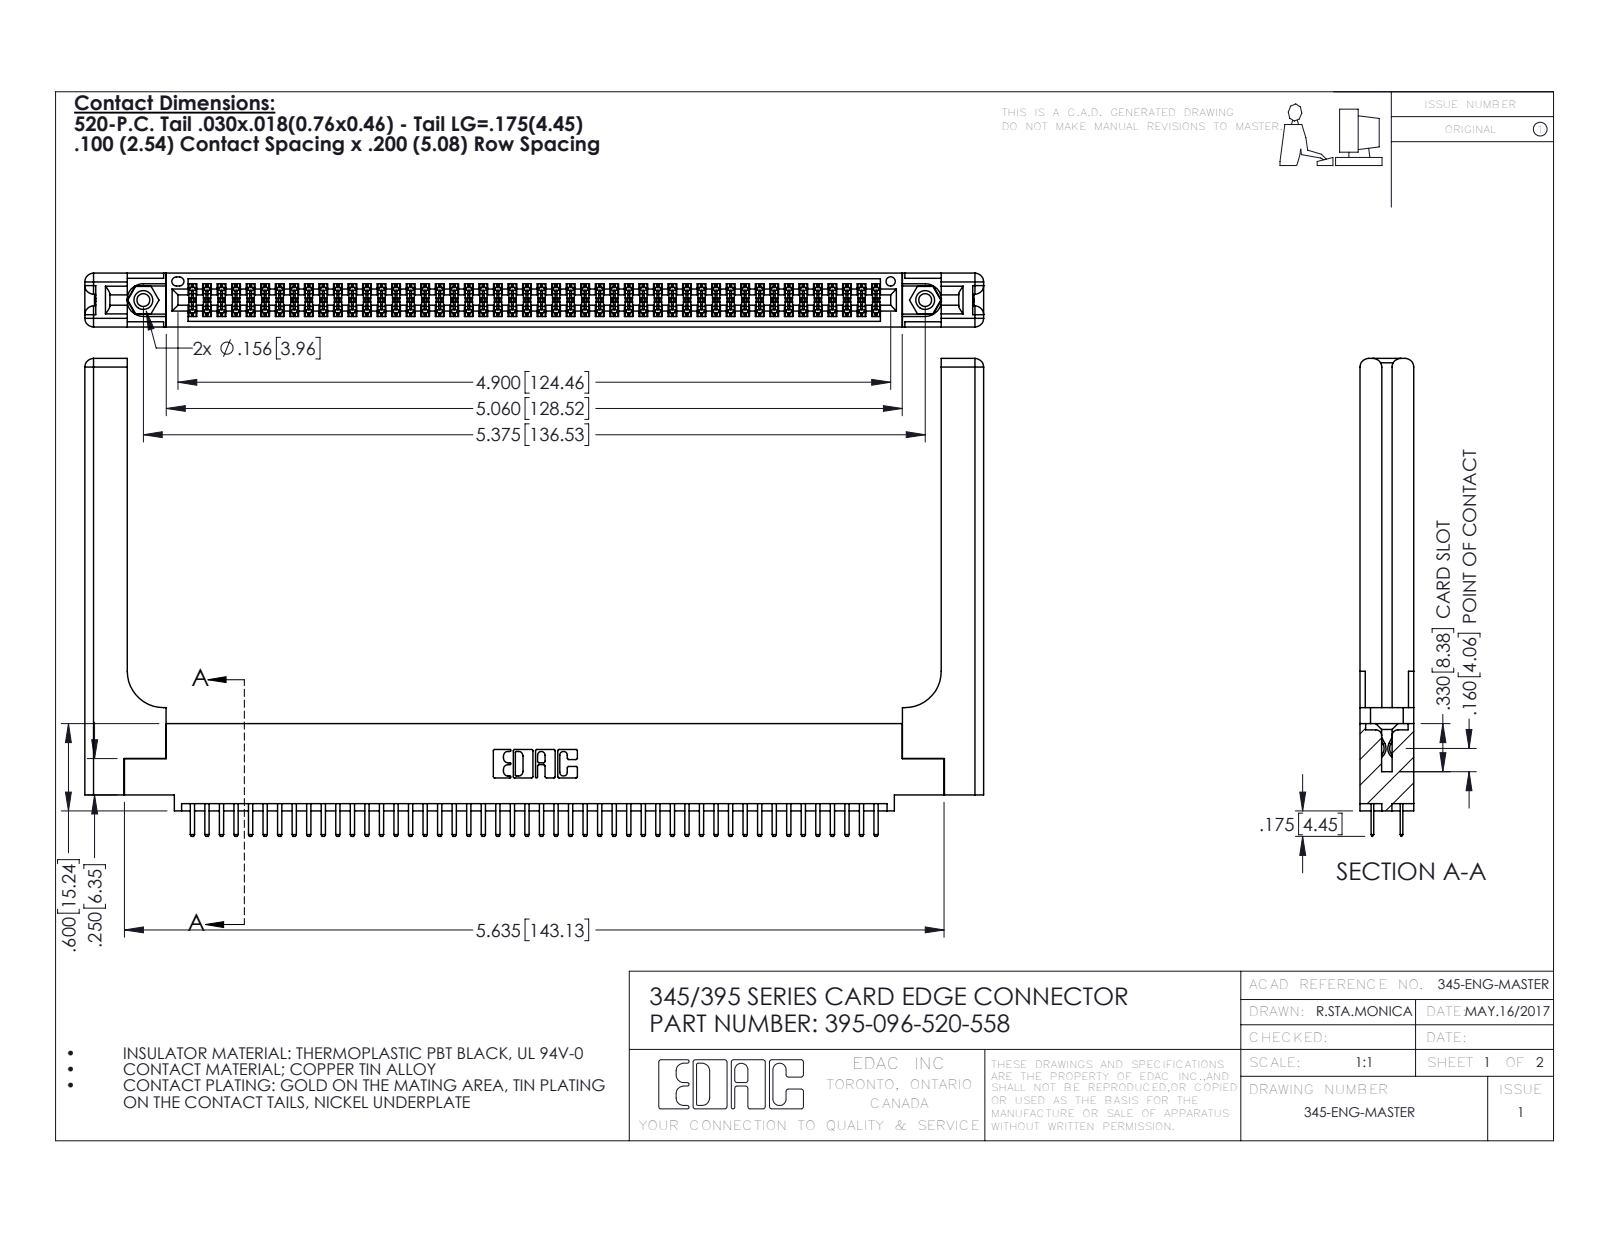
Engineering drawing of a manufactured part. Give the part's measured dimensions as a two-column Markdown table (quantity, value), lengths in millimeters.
| quantity | value |
| --- | --- |
| part name | 345 Part_0.110 Offset - 0.156 Dia-TH; 345-250-001_345-250-001-102; 345-220-058_345-220-058; 345-292-001_345-293-120 (+1 more) |
| STEP written by | SolidWorks 2016 (CONFIG_CONTROL_DESIGN) |
| units | millimeters |
| bodies | 101 solids, 5570 faces (3592 planar, 1918 cylindrical, 60 other) |
| overall size | 156.9 × 83.4 × 9.4 |
| volume | 23 660 mm³ |
| surface area | 27 630 mm² |
| round holes (diameter × count) | 2.3 × 2, 3.2 × 2, 4 × 2, 1.6 × 1 |
| round bosses / shafts (diameter × count) | 3.9 × 2 |
| partial cylindrical surfaces (radius × count) | 0.2 × 144, 0.3 × 100, 0.3 × 22, 1.5 × 16, 0.2 × 6, 0.8 × 6, 0.7 × 3, 0.4 × 2 |
| main face-to-face distances | 1.8, 9.4, 7.6, 5.1, 2.5, 6.9, 0.6, 5.7, 3.8, 3.8 |
| hole center spacings | 6.9, 130.5, 136.5 |
